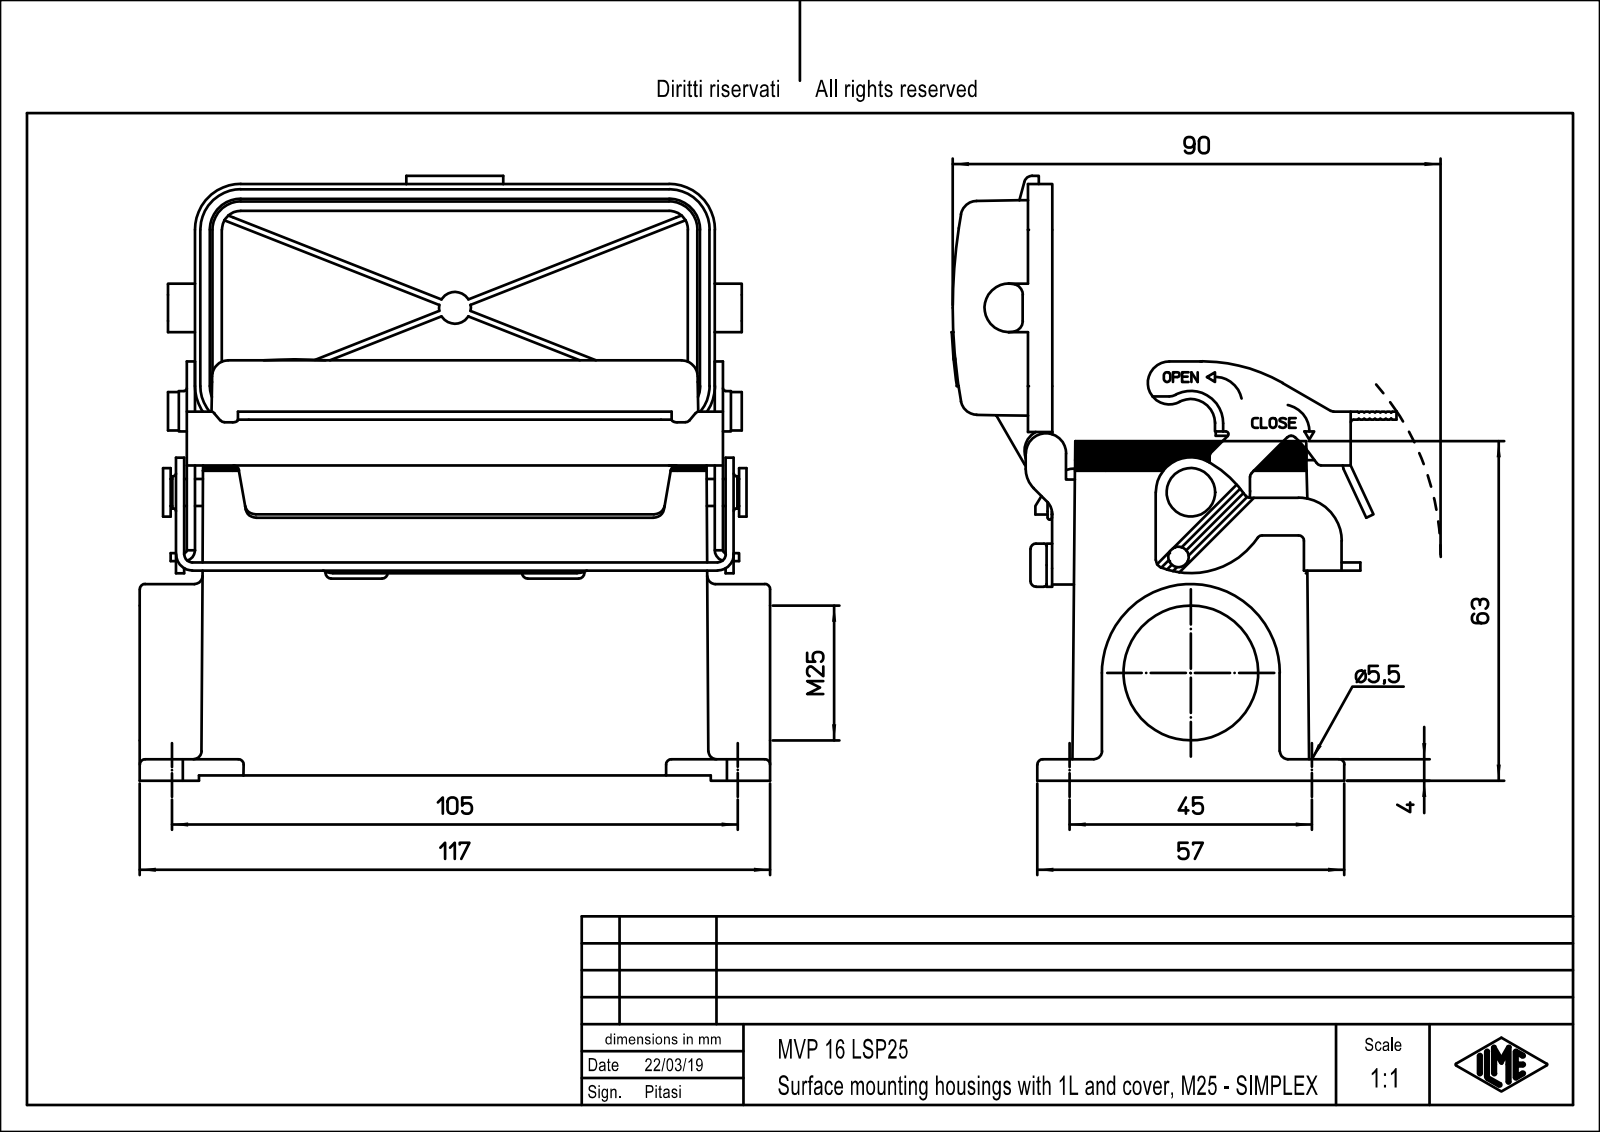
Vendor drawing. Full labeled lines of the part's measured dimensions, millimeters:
Part name (STEP PRODUCT): MVP_16_LSP25
STEP written by: PTC Creo Elements/Direct Modeling 19.0E 27-Jun-2016 (C) Parametric Technology GmbH (AUTOMOTIVE_DESIGN)
Units: millimetres
Bodies: 1 solid, 621 faces (386 planar, 211 cylindrical, 24 other)
Overall size (bounding box): 117 × 112.72 × 79.7
Volume: 131 413 mm³ · Surface area: 77 772 mm²
Round holes (diameter × count): ⌀2.46 ×4, ⌀3 ×4, ⌀5.5 ×4, ⌀20.78 ×1, ⌀25 ×1, ⌀26.78 ×1
Round bosses / shafts (diameter × count): ⌀0.8 ×3, ⌀9 ×1, ⌀8.4 ×1, ⌀8 ×1, ⌀6 ×1, ⌀5 ×1, ⌀2.4 ×1
Partial cylindrical surfaces — rounded edges, fillets, slot ends (radius × count): R2 ×20, R3 ×15, R1.5 ×8, R3.5 ×7, R1 ×5, R6 ×5, R0.5 ×4, R1.8 ×4
Main face-to-face distances: 4, 40.5, 36.5, 44.5, 1.5, 2, 7.5, 3.5, 40.3, 6.65
Hole centre spacings: 16.43, 38.54, 91.69, 98.09, 27, 45, 77.5, 82.07
